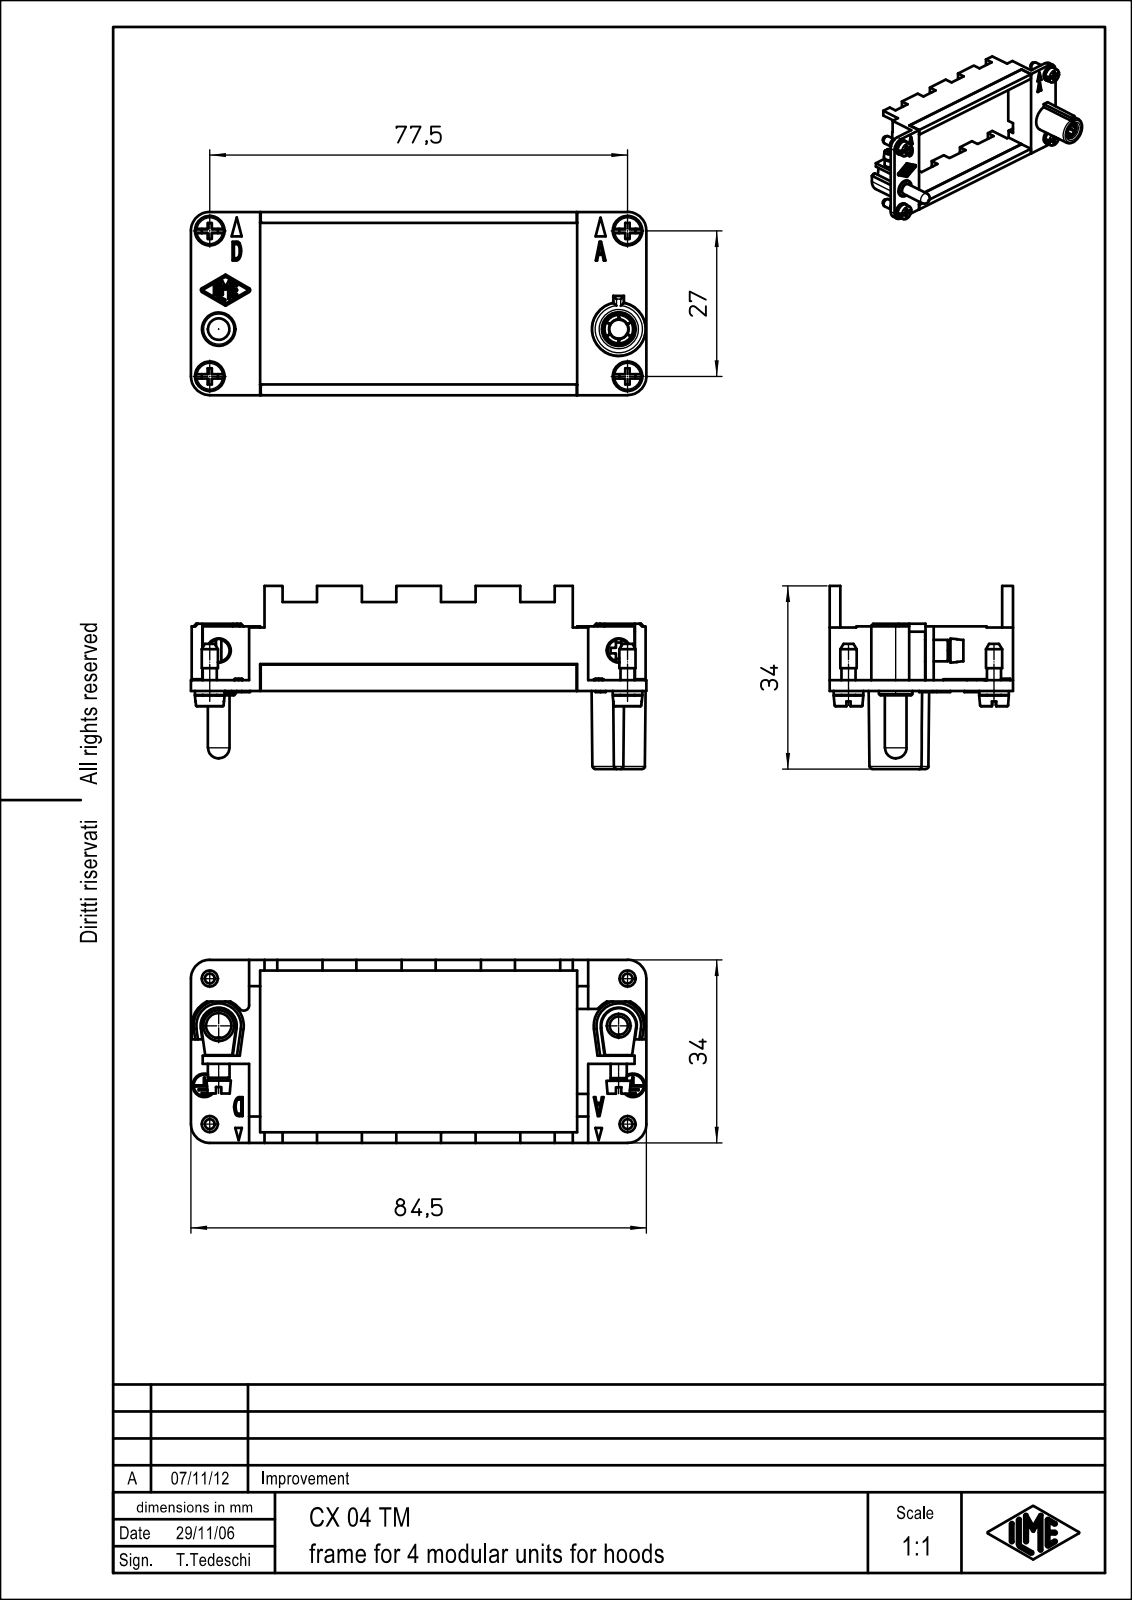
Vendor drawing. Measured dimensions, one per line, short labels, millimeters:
name: CX_04_TM
written by: Creo Elements/Direct Modeling 18.0B 02-Dec-2011 (C) Parametric Technology GmbH (AUTOMOTIVE_DESIGN)
unit: mm
bodies: 1 solid, 633 faces (418 planar, 105 cylindrical, 110 other)
size: 84.5 × 34 × 34
volume: 10 555 mm³; area: 12 161 mm²
holes: 2× ⌀4, 1× ⌀2.5, 1× ⌀3.3, 1× ⌀3.4, 1× ⌀4.2, 1× ⌀4.7, 1× ⌀6.3
bosses: 5× ⌀3, 4× ⌀5.5, 4× ⌀2.6, 2× ⌀4.4, 2× ⌀4, 1× ⌀6.2, 1× ⌀6, 1× ⌀3.5
rounds: 11× R0.17, 4× R3.5, 3× R0.5, 2× R0.13, 2× R0.41, 2× R3.25, 2× R3.35, 2× R5
face distances: 2, 32, 34, 30, 2.05, 60.85, 58.8, 12.7, 62.9, 12.85
hole spacings: 74.2, 11.37, 11.38, 77.64, 77.65, 79.51
